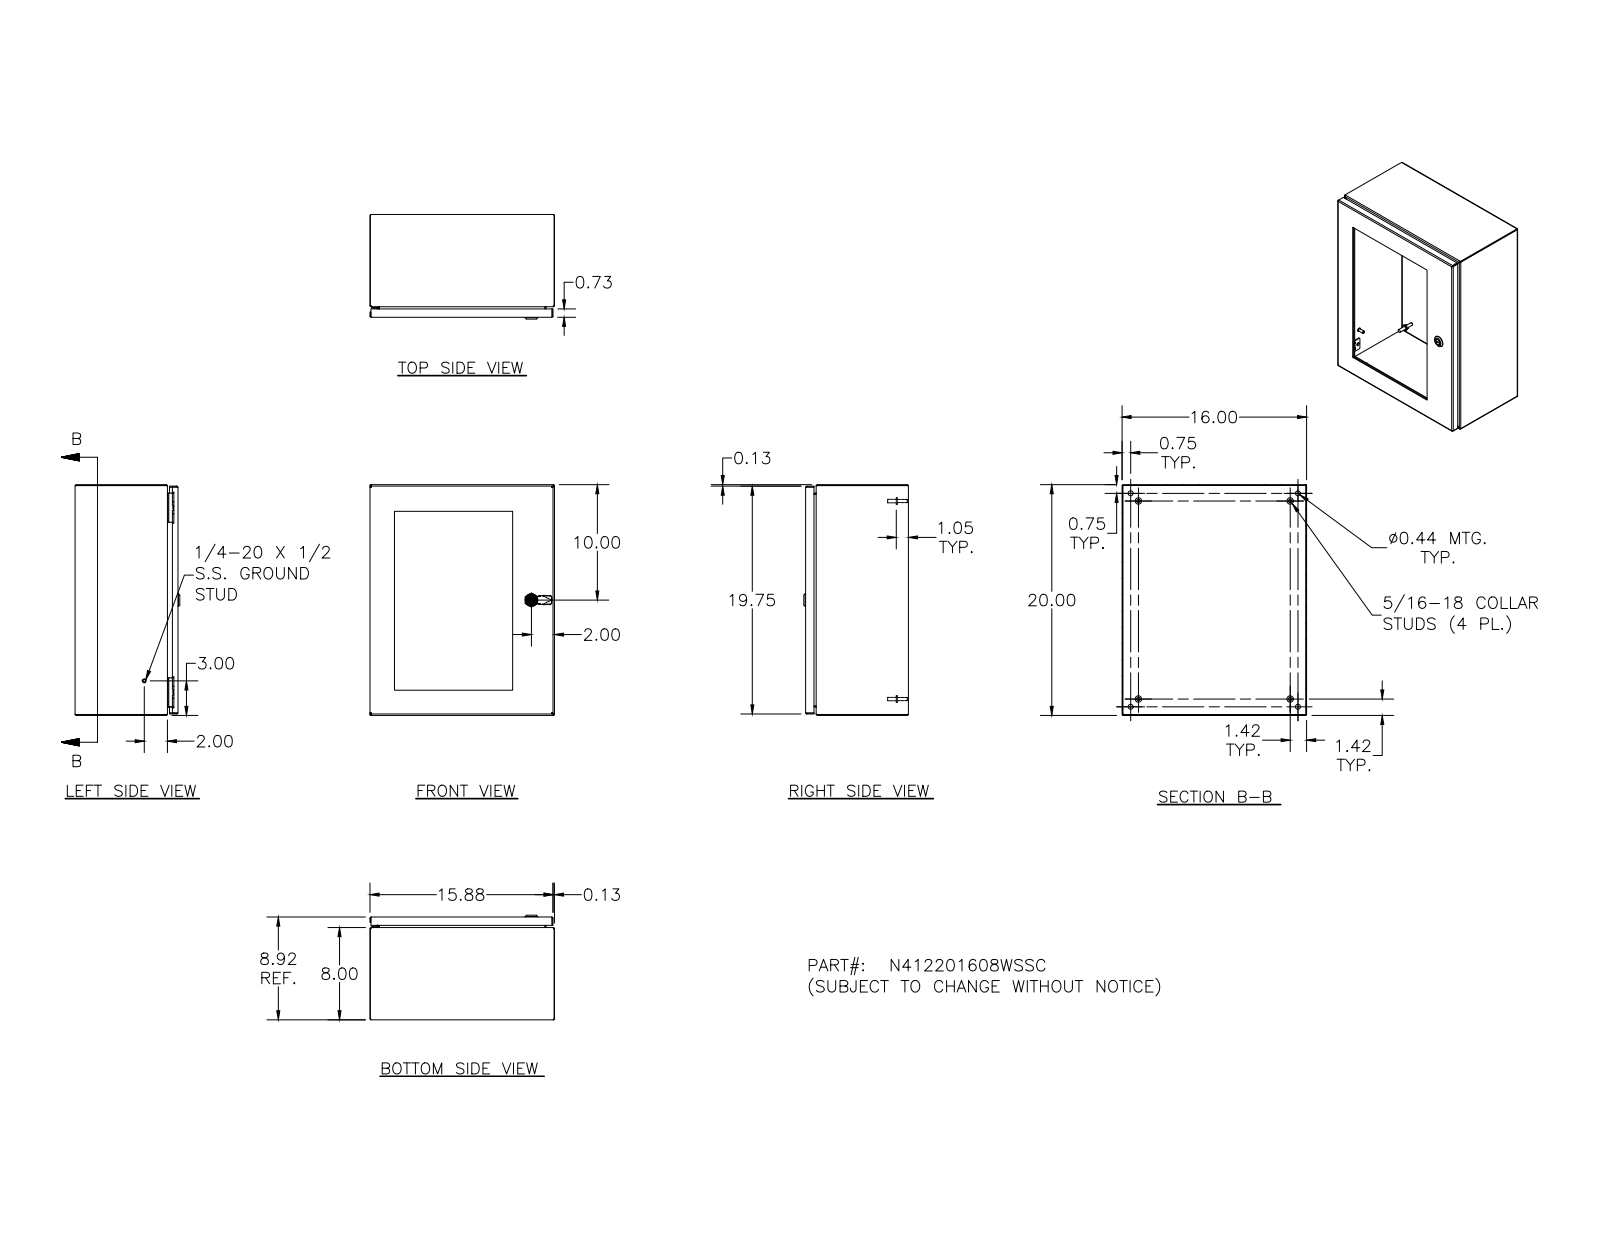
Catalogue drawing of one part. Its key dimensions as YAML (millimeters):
part_name: "N412201608WSSC; N412201608WSSCBKP; N4122016WSSCLID; HFW328176 (+8 more)"
step_written_by: "Autodesk Inventor 2011 (AUTOMOTIVE_DESIGN)"
units: millimeters
bodies: {solids: 66, faces: 1876, planar: 732, cylindrical: 557, other: 587}
overall_size: [508, 406.4, 230.5]
volume: 2299000
surface_area: 1907000
round_holes:
  - {diameter: 4, count: 16}
  - {diameter: 7.1, count: 14}
  - {diameter: 2.4, count: 4}
  - {diameter: 3.9, count: 4}
  - {diameter: 4.2, count: 4}
  - {diameter: 4.4, count: 4}
  - {diameter: 4.8, count: 4}
  - {diameter: 11.1, count: 4}
  - {diameter: 4.7, count: 1}
  - {diameter: 5, count: 1}
  - {diameter: 8, count: 1}
  - {diameter: 10, count: 1}
round_bosses_or_shafts:
  - {diameter: 4.8, count: 14}
  - {diameter: 6.4, count: 13}
  - {diameter: 6.4, count: 10}
  - {diameter: 14.3, count: 4}
  - {diameter: 9.1, count: 4}
  - {diameter: 8.1, count: 4}
  - {diameter: 7.6, count: 4}
  - {diameter: 7, count: 4}
partial_cylinders:
  - {radius: 0.8, count: 34}
  - {radius: 1.3, count: 26}
  - {radius: 2.7, count: 24}
  - {radius: 0.4, count: 18}
  - {radius: 3.2, count: 16}
  - {radius: 0.5, count: 9}
  - {radius: 0.8, count: 8}
  - {radius: 4, count: 4}
face_to_face_distances: [1.9, 224.6, 222.7, 404.5, 506.1, 6.4, 218.3, 216.4, 402.6, 406.4]
hole_center_spacings: [101.6, 203.2, 309.3, 406.4, 158, 218.1, 254.9, 292.1]
